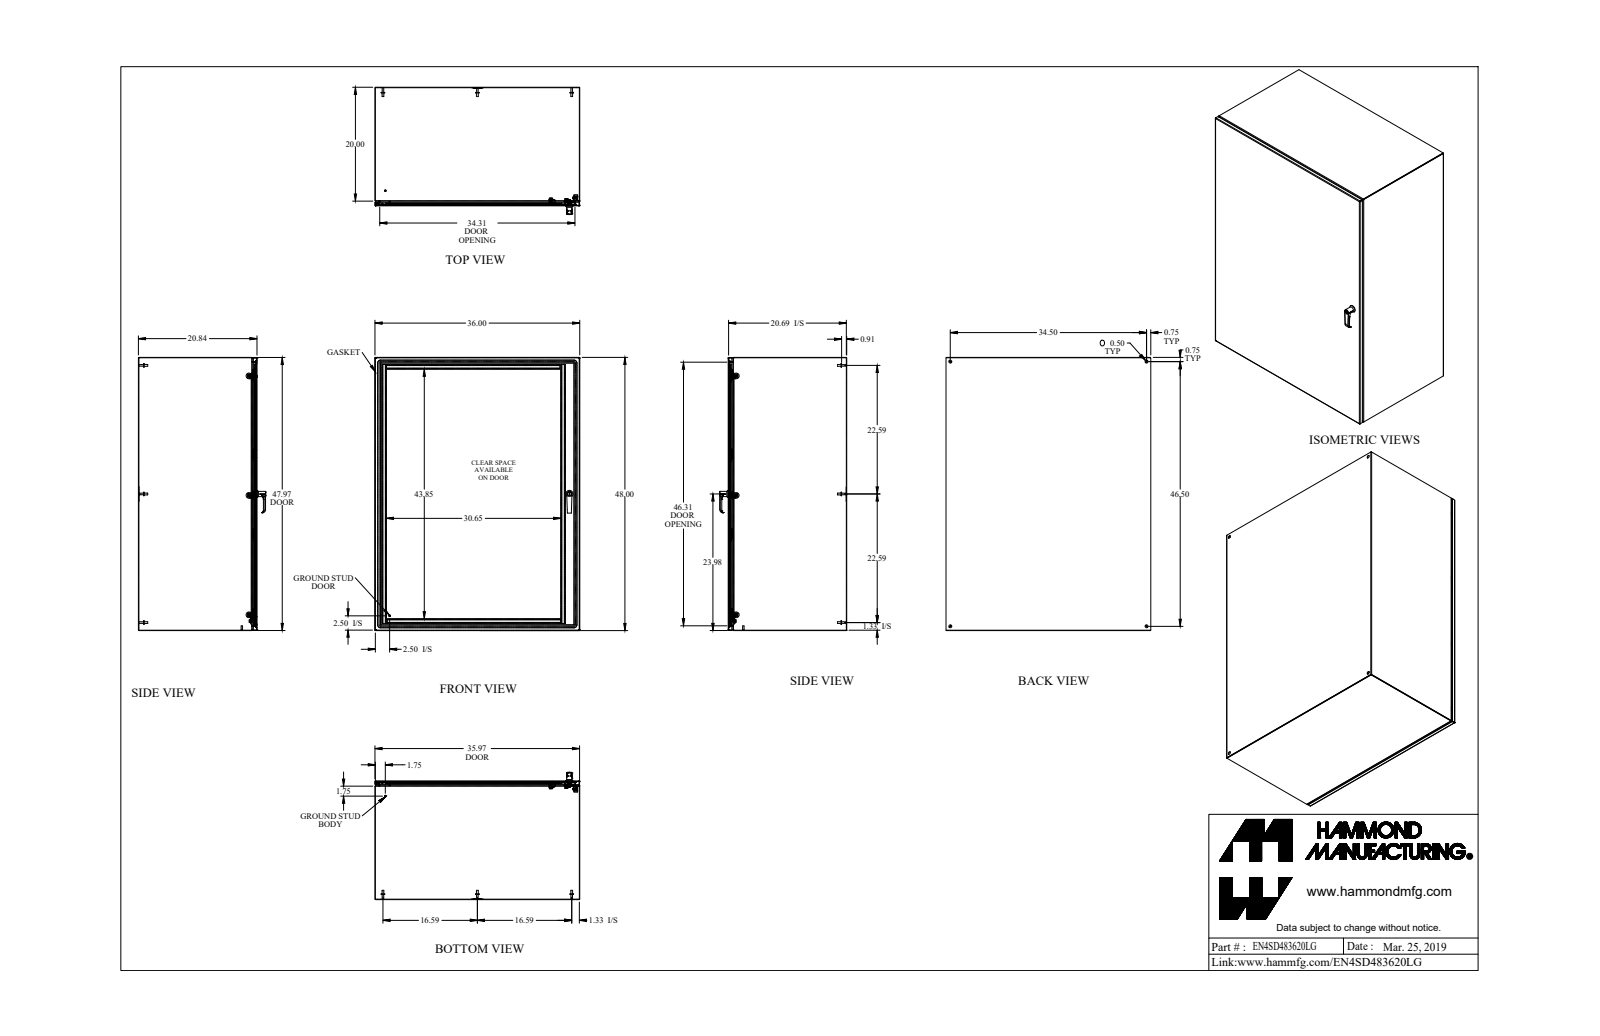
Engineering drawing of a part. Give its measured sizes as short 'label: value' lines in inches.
name: EN4SD483620LG
written by: SolidWorks 2018 (AUTOMOTIVE_DESIGN)
unit: in
bodies: 63 solids, 1719 faces (757 planar, 632 cylindrical, 330 other)
size: 48 × 36 × 22.367
volume: 551.1 in³; area: 15 408 in²
holes: 6× ⌀0.176, 4× ⌀0.196, 4× ⌀0.5, 3× ⌀0.25, 3× ⌀0.265, 3× ⌀0.413, 2× ⌀0.256, 2× ⌀0.313, 2× ⌀0.394, 1× ⌀0.172, 1× ⌀0.24, 1× ⌀0.242
bosses: 8× ⌀0.313, 8× ⌀0.27, 7× ⌀0.25, 6× ⌀0.625, 6× ⌀0.375, 6× ⌀0.156, 3× ⌀1, 3× ⌀0.625
rounds: 24× R0.043, 24× R0.081, 21× R0.062, 18× R0.036, 18× R0.108, 15× R0.03, 10× R0.094, 9× R0.016
face distances: 0.072, 20.765, 35.928, 20.693, 20.837, 35.856, 36, 0.072, 47.856, 47.928
hole spacings: 41.969, 0.787, 20.981, 20.988, 21, 33.504, 34.5, 46.5
